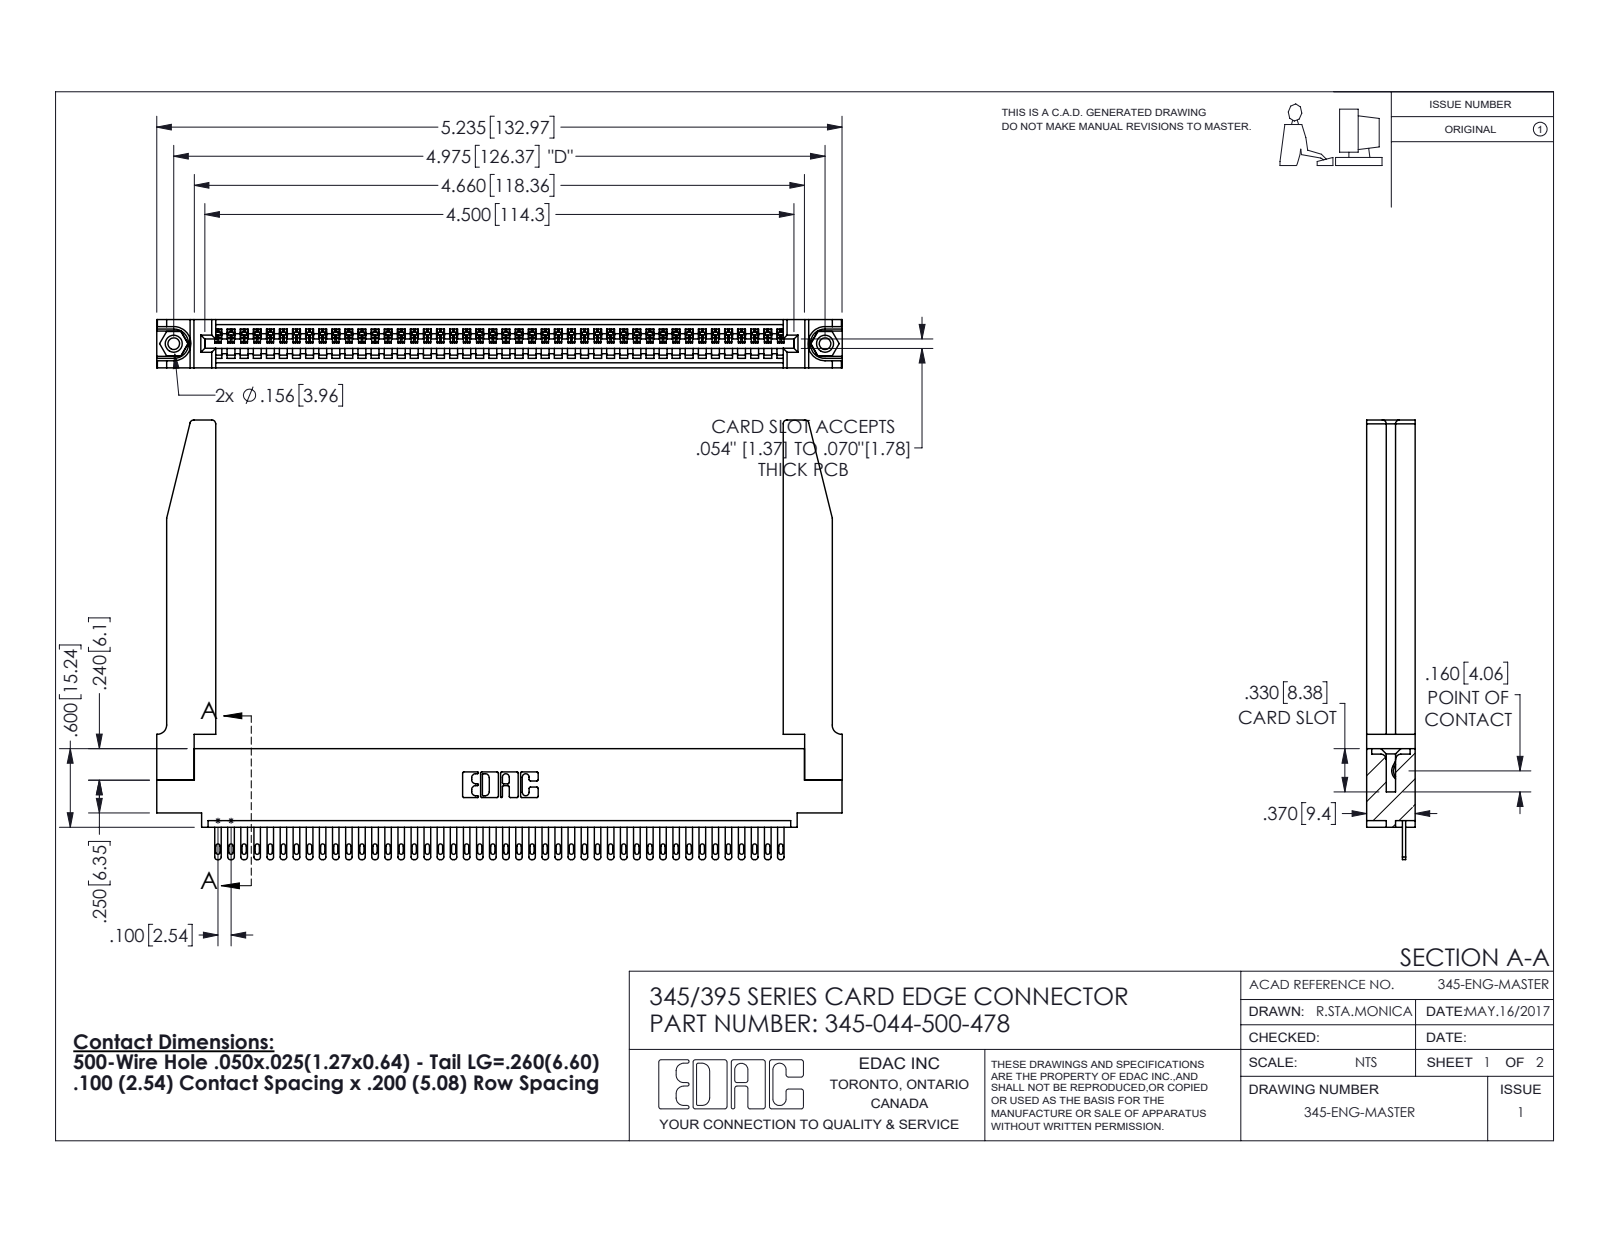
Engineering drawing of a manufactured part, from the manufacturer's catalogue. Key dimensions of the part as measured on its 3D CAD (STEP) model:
Part name (STEP PRODUCT): 345-250-001_345-250-001-102; 345-044-500-478; 345-220-078_345-220-078; 345-292-001_345-293-100 (+1 more)
STEP written by: SolidWorks 2016 (CONFIG_CONTROL_DESIGN)
Units: inches
Bodies: 49 solids, 2740 faces (1722 planar, 966 cylindrical, 52 other)
Overall size (bounding box): 5.236 × 3.357 × 0.37
Volume: 1.243 in³ · Surface area: 36.89 in²
Round holes (diameter × count): ⌀0.089 ×2, ⌀0.125 ×2, ⌀0.156 ×2, ⌀0.064 ×1
Round bosses / shafts (diameter × count): ⌀0.155 ×2
Partial cylindrical surfaces — rounded edges, fillets, slot ends (radius × count): R0.006 ×88, R0.016 ×88, R0.02 ×88, R0.01 ×22, R0.03 ×8, R0.007 ×6, R0.031 ×6, R0.026 ×3
Main face-to-face distances: 0.37, 0.072, 0.298, 0.098, 0.272, 0.025, 0.2, 0.225, 0.148, 0.15
Hole centre spacings: 0.27, 4.739, 4.975
